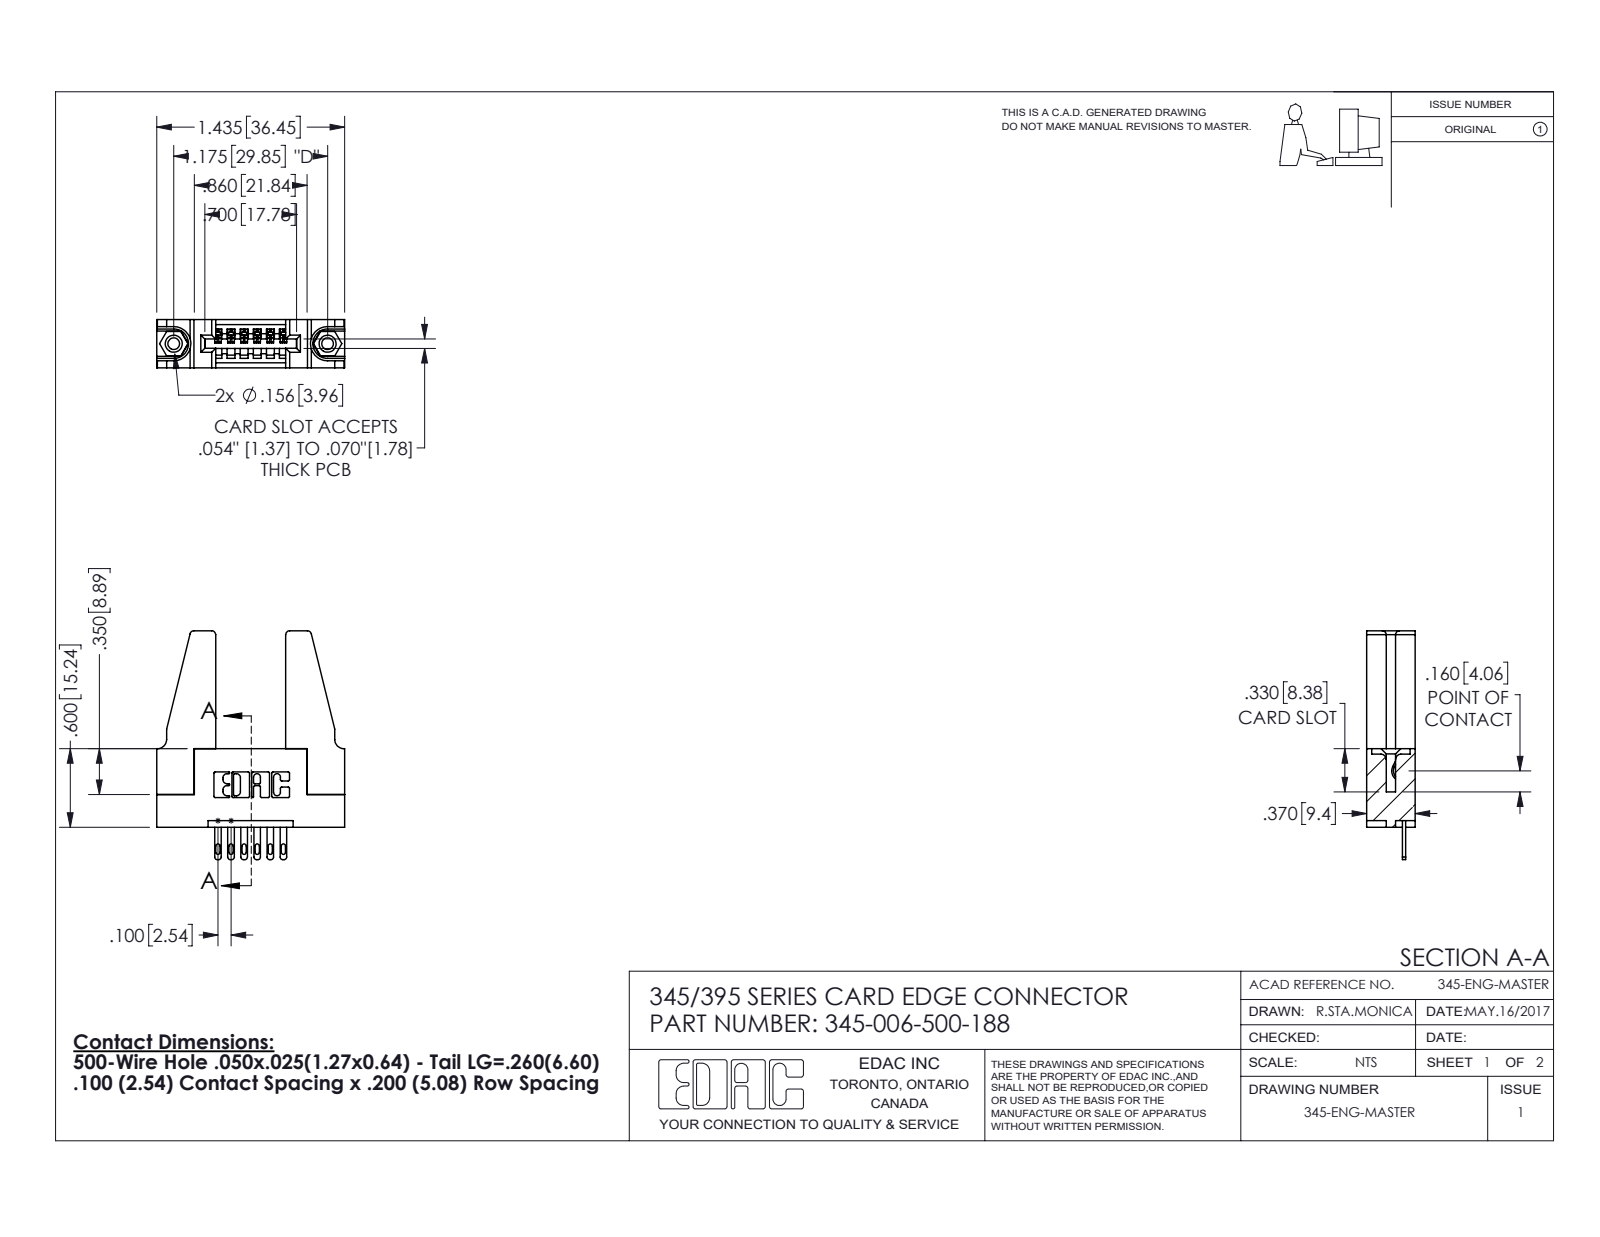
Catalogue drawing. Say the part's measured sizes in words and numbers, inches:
The part is named "345-250-001_345-250-001-102; 345-292-001_345-293-100; 345-006-500-188; 345 Part_Flush Mounting Lugs - 0.156 Dia-TH (+1 more)". Its 3-D file was written by "SolidWorks 2016 (CONFIG_CONTROL_DESIGN)". It is 11 solids with 574 faces: 356 planar, 202 cylindrical and 16 other. Overall it measures 1.747 by 1.436 by 0.37 inches. Its volume is 0.392 cubic inches and its surface area 10.65 square inches. Round holes: 2 of diameter 0.089, 2 of diameter 0.125, 2 of diameter 0.156, 1 of diameter 0.064. Round bosses or shafts: 2 of diameter 0.155. Partial cylindrical surfaces (rounded edges, fillets, slot ends): 22 of radius 0.01, 12 of radius 0.006, 12 of radius 0.016, 12 of radius 0.02, 8 of radius 0.03, 6 of radius 0.007, 6 of radius 0.031, 3 of radius 0.026. The main face-to-face distances are 0.37, 0.2, 0.072, 0.298, 0.698, 0.15, 0.148, 0.35, 0.098, 0.272. The hole center spacings are 0.27, 0.946, 1.175.
